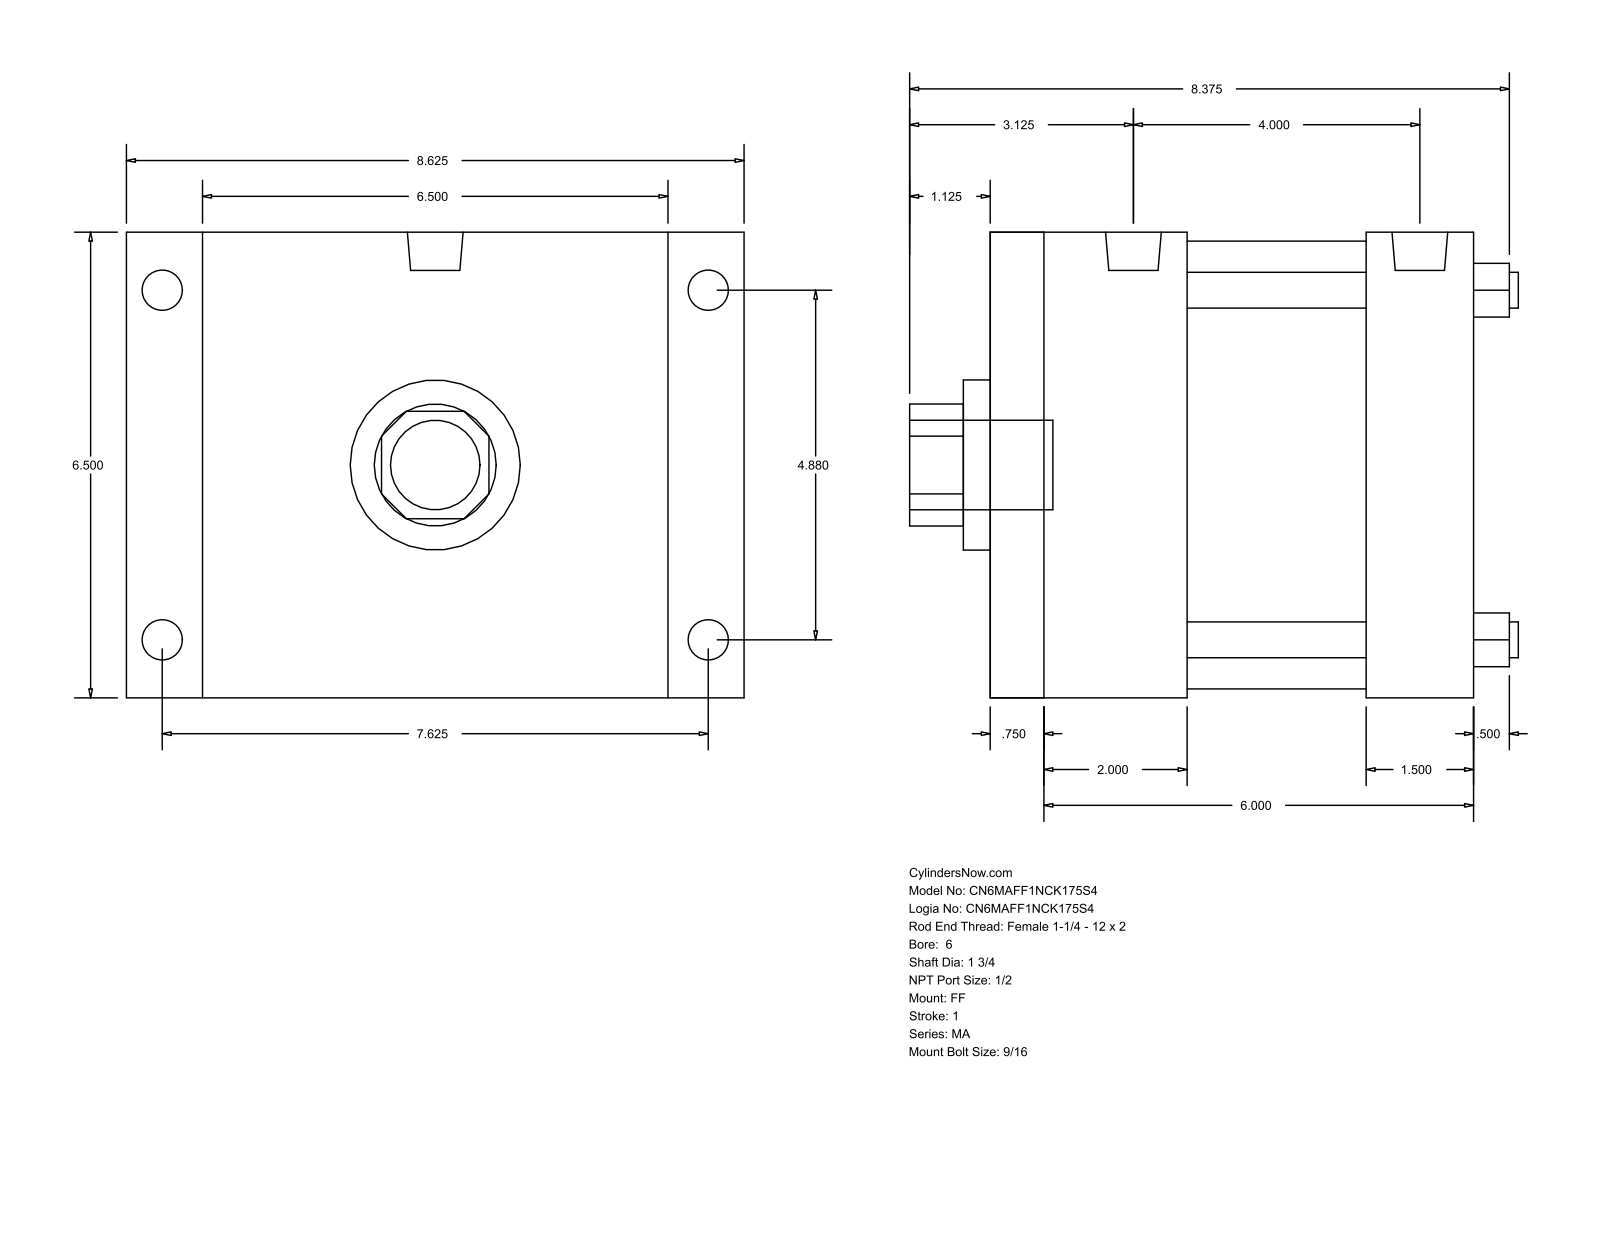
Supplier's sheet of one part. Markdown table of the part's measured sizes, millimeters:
| quantity | value |
| --- | --- |
| part name | MA_FF__0600_1.75 |
| STEP written by | GSSL Pune (CONFIG_CONTROL_DESIGN) |
| units | millimeters |
| bodies | 0 solids, 92 faces (64 planar, 28 cylindrical, 0 other) |
| overall size | 219.07 × 215.9 × 165.1 |
| round holes (diameter × count) | 12.7 × 4, 44.45 × 1, 60.33 × 1, 158.75 × 1 |
| round bosses / shafts (diameter × count) | 17.46 × 4, 14.29 × 4, 19.77 × 2, 31.75 × 1 |
| partial cylindrical surfaces (radius × count) | 21.63 × 1 |
| main face-to-face distances | 165.1, 171.46, 19.05, 152.41, 38.1, 50.8, 69.85, 101.61, 133.36, 114.31 |
| hole center spacings | 87.65, 123.96, 175.31 |
